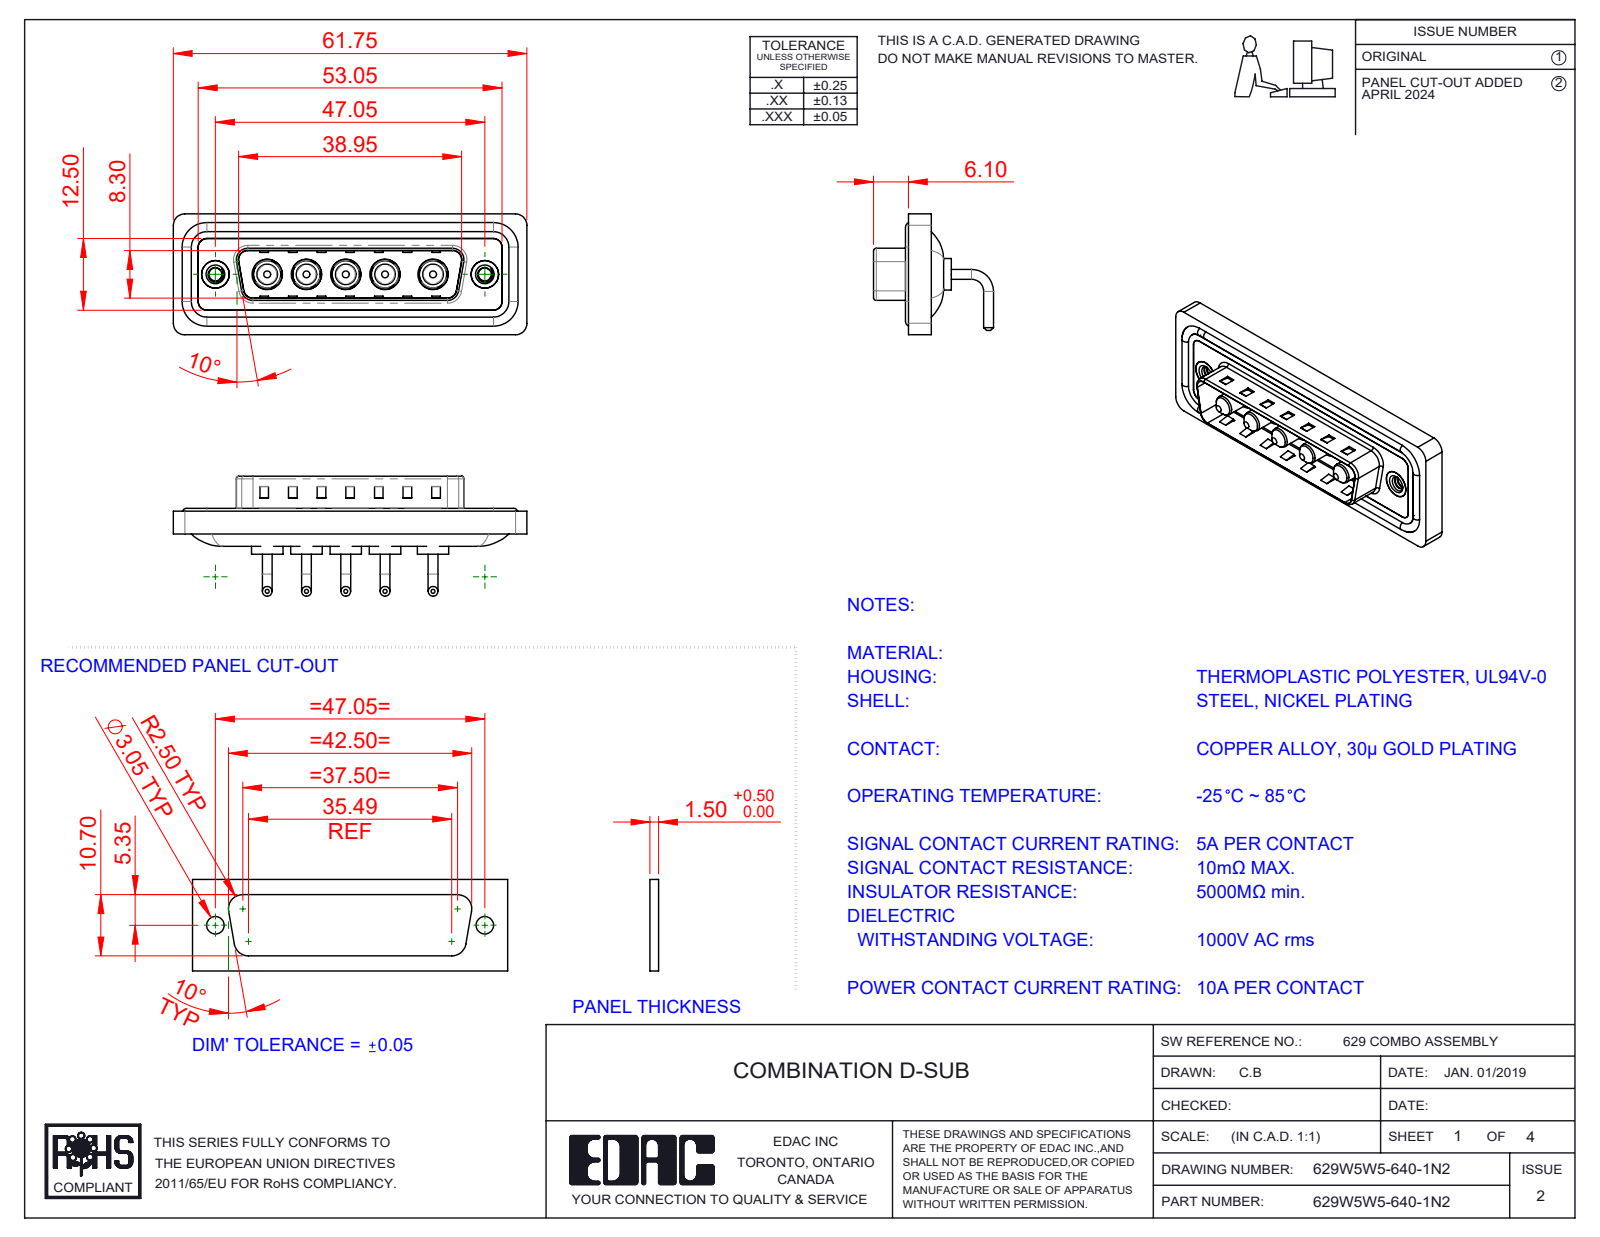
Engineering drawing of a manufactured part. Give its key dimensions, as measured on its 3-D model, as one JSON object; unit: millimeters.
{"part_name": "Power Pin_10A RA; 629Combo Shell Rear_25 Contacts; 629Combo Shell Front_25 Contacts; 629Combo Waterproof Housing_25 Contacts (+3 more)", "step_written_by": "SolidWorks 2023 (CONFIG_CONTROL_DESIGN)", "units": "millimeters", "bodies": {"solids": 17, "faces": 698, "planar": 259, "cylindrical": 293, "other": 146}, "overall_size": [61.75, 21.1, 20.95], "volume_mm3": 7523, "surface_area_mm2": 12018, "round_holes": [[4.85, 5], [5.3, 5], [2.26, 2], [4, 2], [4.8, 2], [5, 2]], "round_bosses_or_shafts": [[1.7, 10], [5.5, 5], [5.2, 5], [4.75, 5], [3.75, 5], [3.6, 5], [1.6, 4], [4.9, 2]], "partial_cylinders_radius": [[1.5, 18], [2, 18], [0.5, 8], [1.6, 8], [2.1, 5], [0.25, 4], [0.6, 4], [0.65, 4]], "face_to_face_distances": [0.4, 2.9, 0.8, 4.5, 4.1, 1.5, 1.1, 2.1, 3.1, 6], "hole_center_spacings": [6.86, 13.73, 6.85, 6.87, 8.37, 8.38, 9.04, 9.05]}
